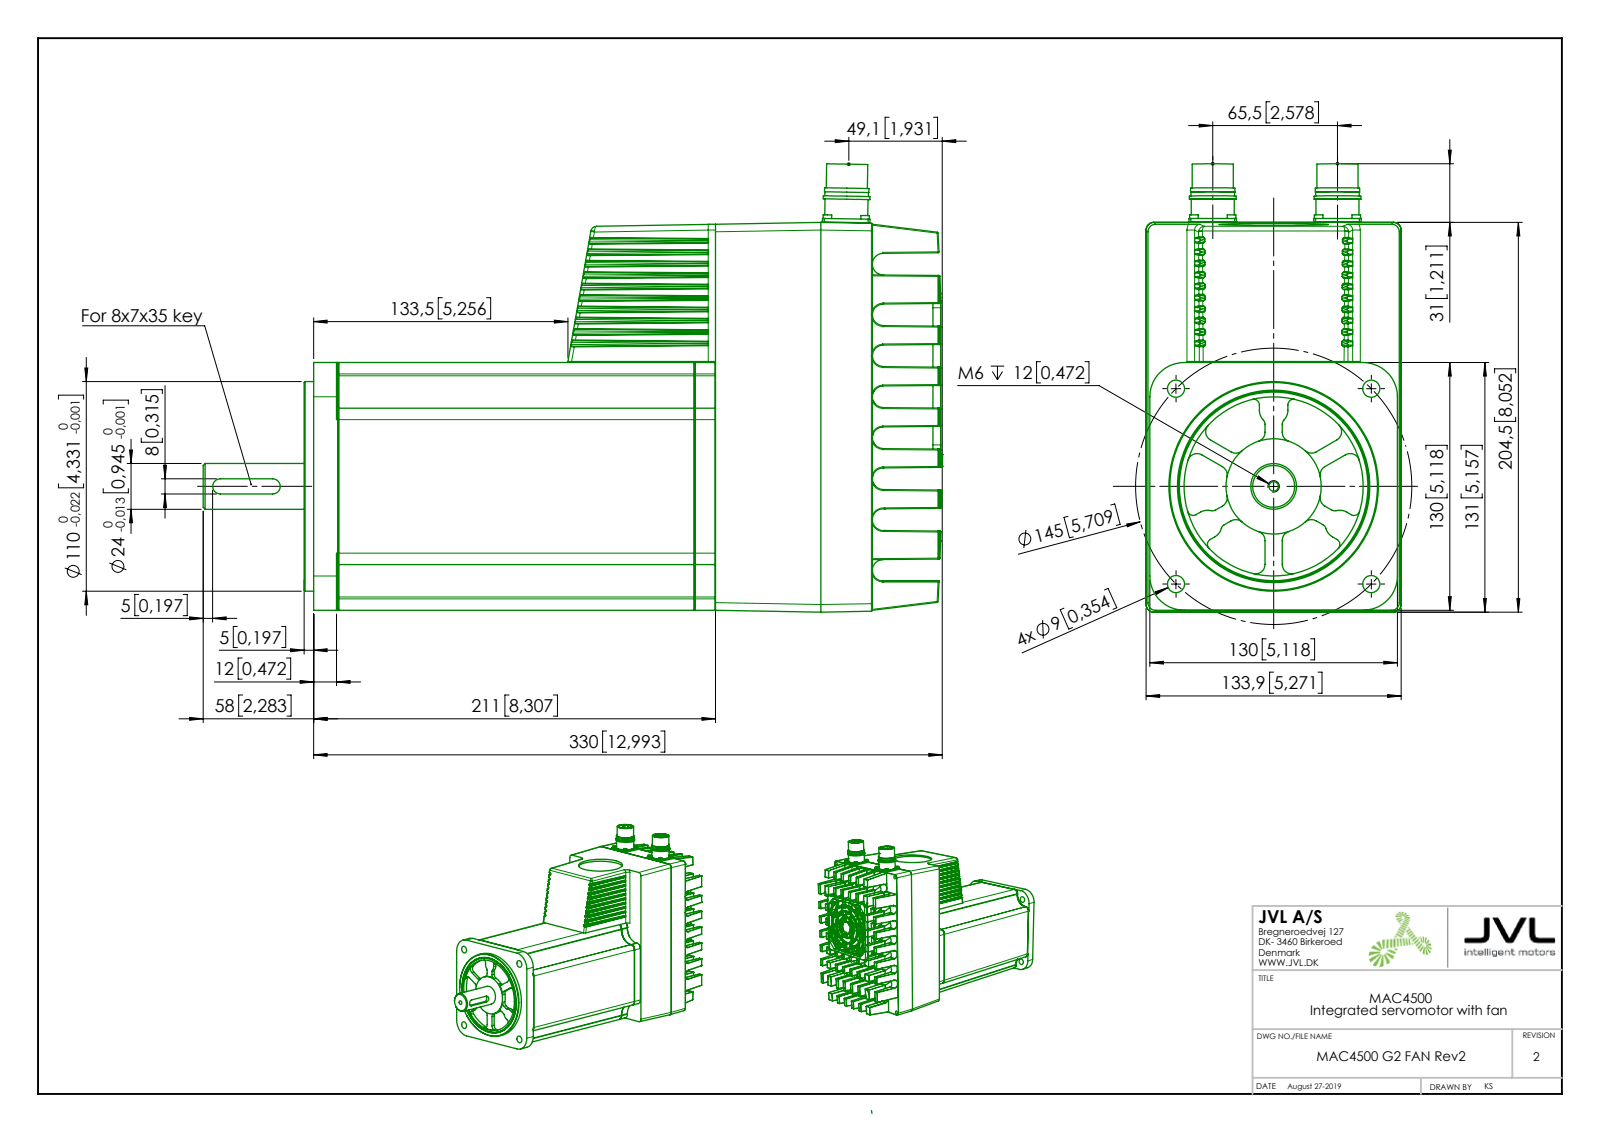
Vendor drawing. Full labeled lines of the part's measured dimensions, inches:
Part name (STEP PRODUCT): MAC 4500 G2 FAN Rev2; M23 female; M23 male; Rear flange S (+7 more)
STEP written by: SolidWorks 2018 (AUTOMOTIVE_DESIGN)
Units: inches
Bodies: 10 solids, 2452 faces (824 planar, 1051 cylindrical, 577 other)
Overall size (bounding box): 15.283 × 9.263 × 5.271
Volume: 366.4 in³ · Surface area: 790.8 in²
Round holes (diameter × count): ⌀0.098 ×8, ⌀0.079 ×5, ⌀0.169 ×4, ⌀0.354 ×4, ⌀0.787 ×2, ⌀0.795 ×2, ⌀0.181 ×1, ⌀0.197 ×1, ⌀1.114 ×1, ⌀1.744 ×1, ⌀2.269 ×1, ⌀2.402 ×1
Round bosses / shafts (diameter × count): ⌀0.177 ×8, ⌀0.079 ×5, ⌀0.965 ×2, ⌀0.917 ×2, ⌀0.902 ×2, ⌀0.89 ×2, ⌀0.85 ×2, ⌀4.409 ×1
Partial cylindrical surfaces — rounded edges, fillets, slot ends (radius × count): R0.02 ×288, R0.012 ×94, R0.031 ×40, R0.197 ×18, R0.157 ×16, R0.118 ×15, R0.024 ×10, R0.236 ×8
Main face-to-face distances: 2.177, 5.118, 7.362, 7.795, 9.972, 0.433, 2.61, 7.874, 8.307, 5.27
Hole centre spacings: 0.557, 0.787, 2.578, 0.236, 0.278, 1.113, 2.219, 2.696
